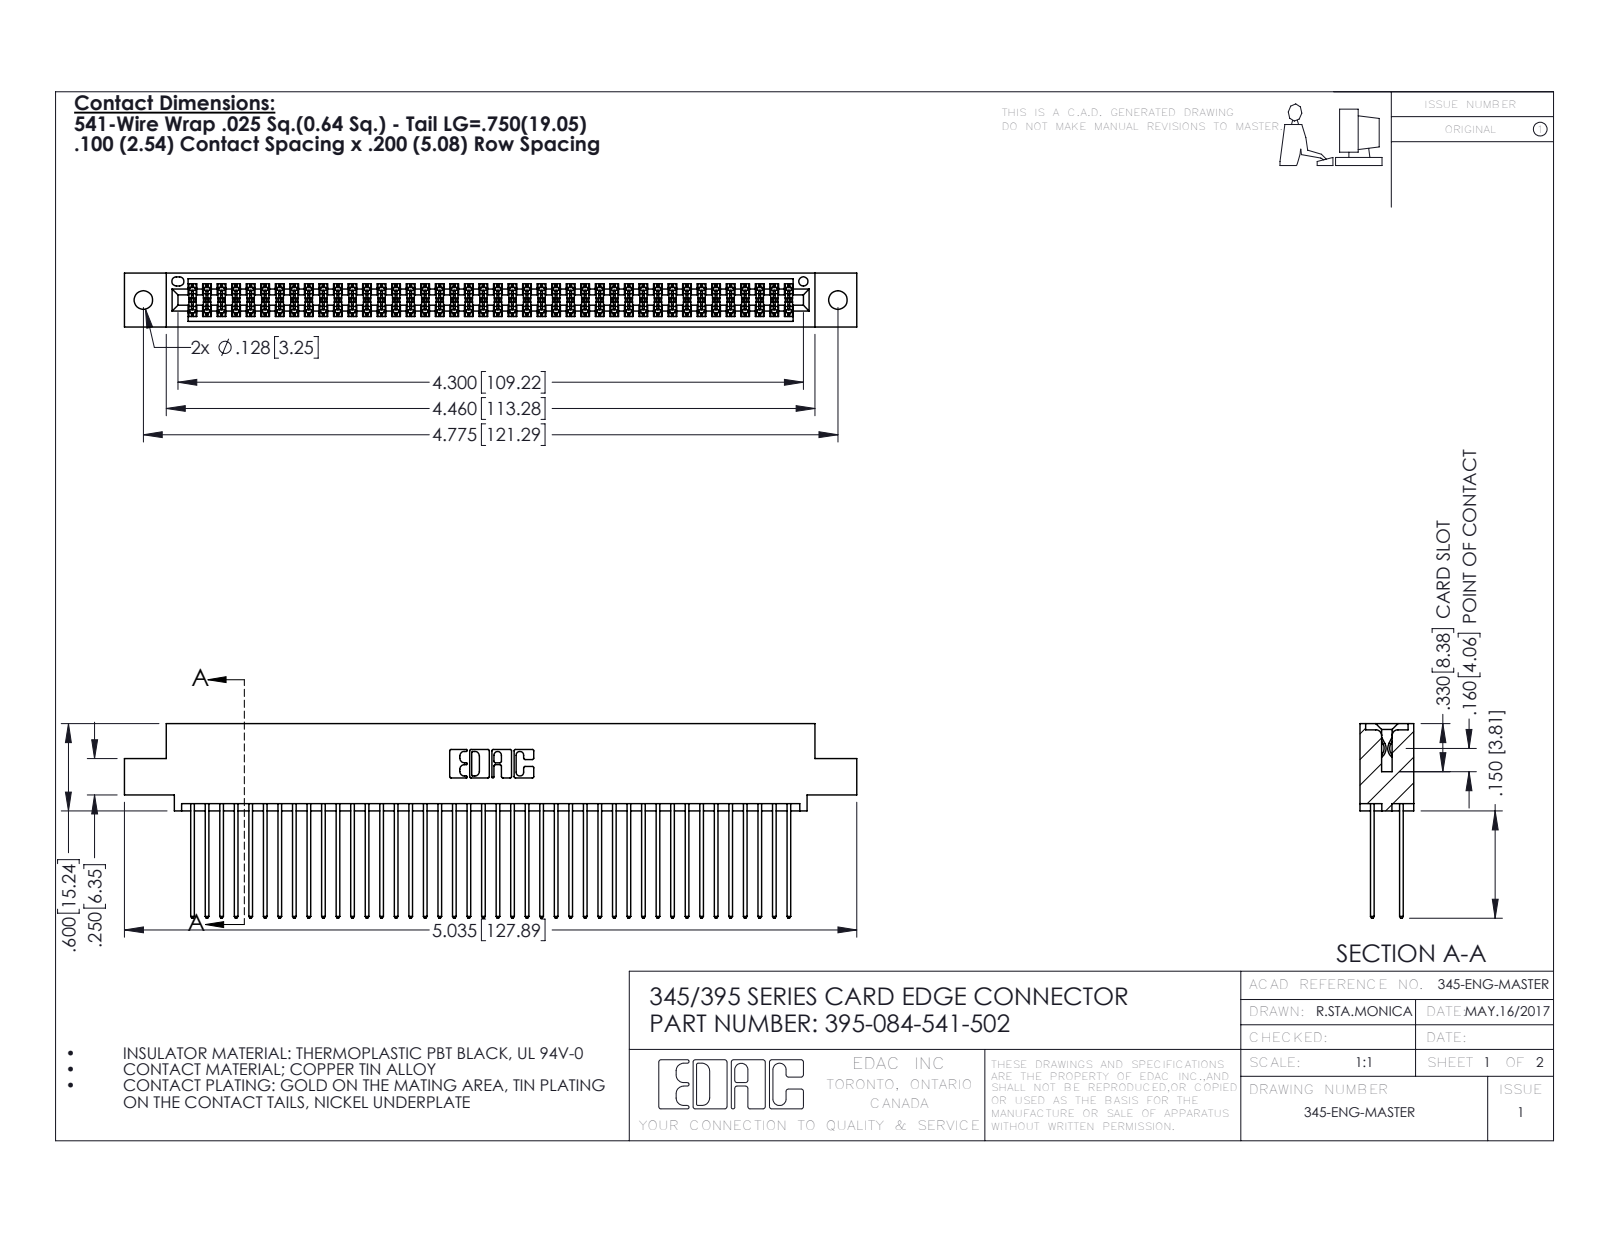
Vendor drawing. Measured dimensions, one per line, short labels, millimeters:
name: 345-292-001_345-293-141; 395-084-541-502; 345 Part_0.110 Offset - 0.128 Dia
written by: SolidWorks 2016 (CONFIG_CONTROL_DESIGN)
unit: mm
bodies: 85 solids, 4330 faces (2856 planar, 1474 cylindrical, 0 other)
size: 127.9 × 34 × 9.4
volume: 12 800 mm³; area: 21 000 mm²
holes: 2× ⌀3.3, 1× ⌀1.6
rounds: 126× R0.2, 84× R0.3, 22× R0.3, 6× R0.2, 6× R0.8, 3× R0.7, 2× R0.4, 2× R0.5
face distances: 7.6, 1.8, 5.1, 2.5, 6.9, 0.6, 5.7, 9.4, 4.4, 3.8
hole spacings: 6.9, 115.3, 121.3
